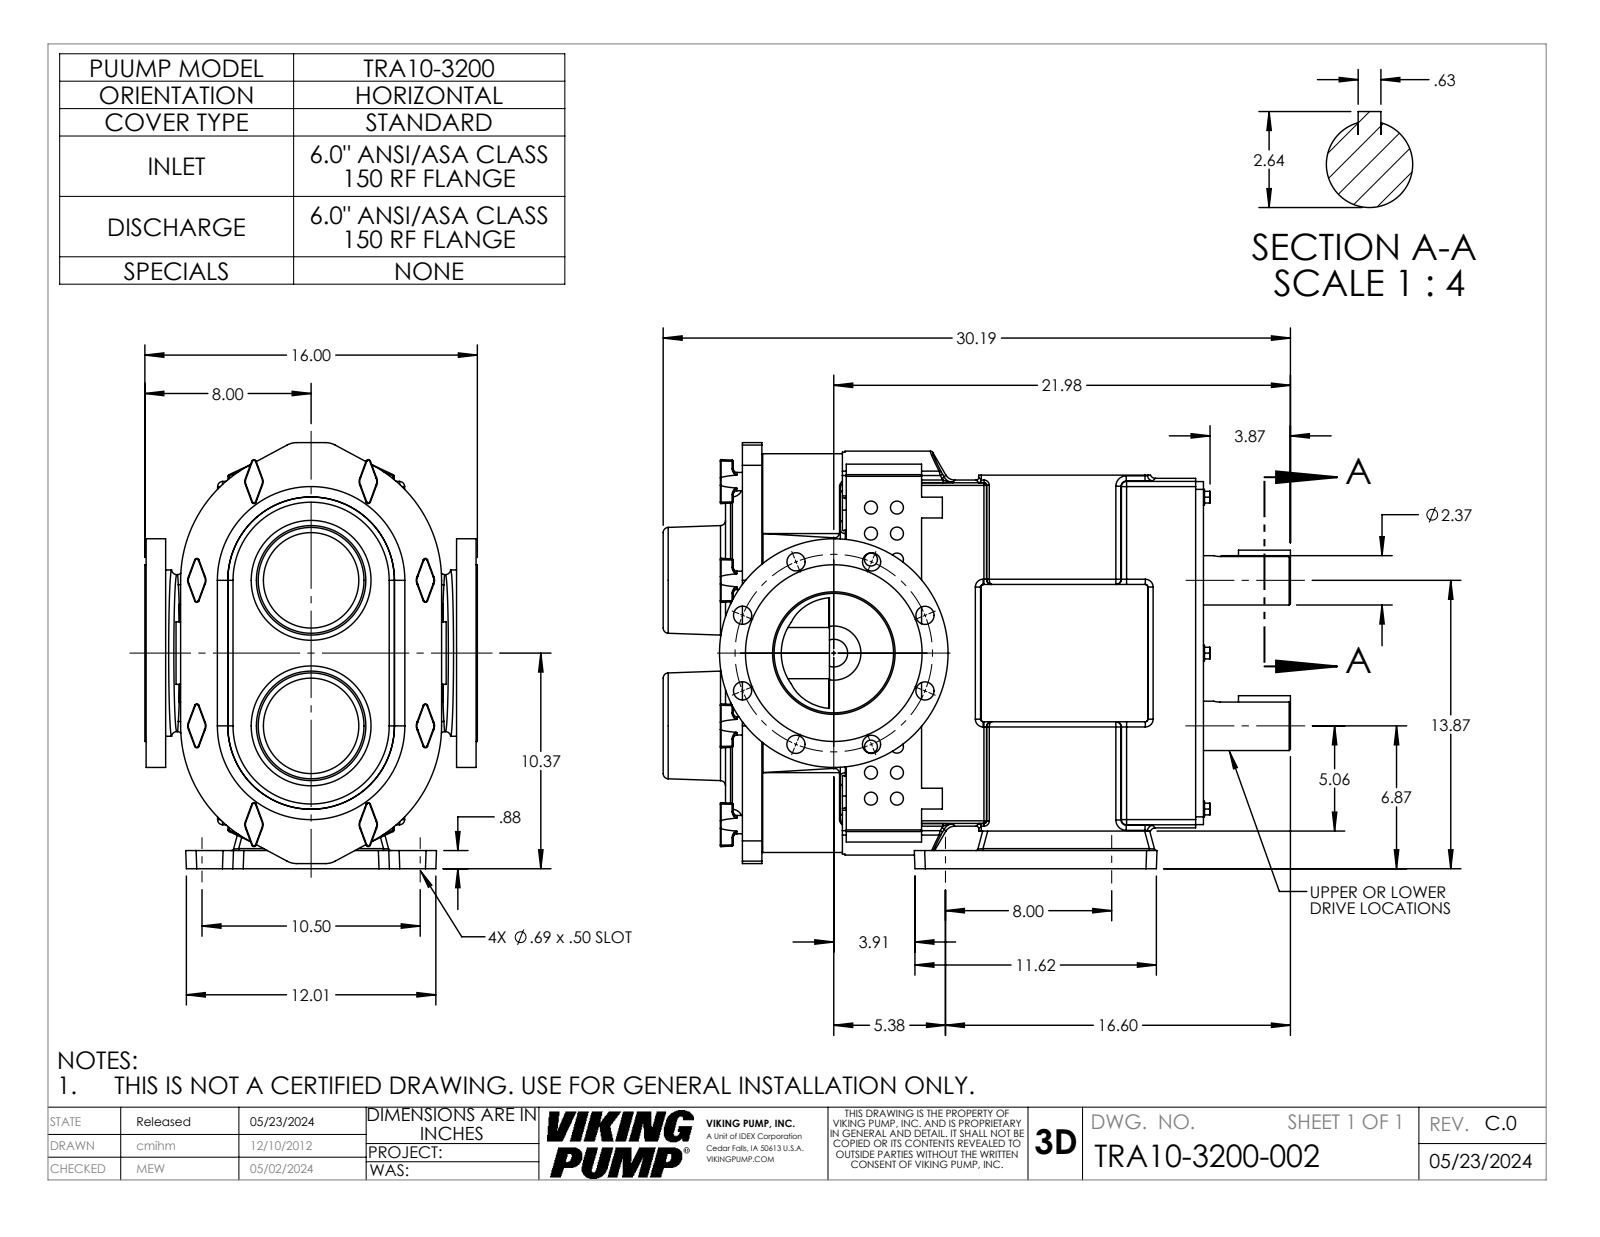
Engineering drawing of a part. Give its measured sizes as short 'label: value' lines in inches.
name: WA3200RCN-60F-60F-00; TRA10-3200-GEARBOX; TRA10-3200-COVER-STD; TRA10-3200-002
written by: SolidWorks 2023 (AUTOMOTIVE_DESIGN)
unit: in
bodies: 3 solids, 1340 faces (342 planar, 476 cylindrical, 522 other)
size: 30.186 × 20.498 × 16
volume: 3 159 in³; area: 3 784 in²
holes: 16× ⌀0.625, 8× ⌀0.313, 8× ⌀0.875, 4× ⌀0.531, 4× ⌀0.687, 2× ⌀0.437, 2× ⌀0.616, 2× ⌀0.625, 2× ⌀4.002, 2× ⌀4.878
bosses: 8× ⌀0.88, 6× ⌀0.75, 2× ⌀4.865, 2× ⌀2.374, 1× ⌀11, 1× ⌀8.5, 1× ⌀8, 1× ⌀7.55
rounds: 66× R0.25, 58× R0.125, 32× R0.03, 32× R0.06, 14× R0.5, 8× R0.344, 4× R0.029, 4× R0.089
face distances: 0.06, 1, 3.5, 11.5, 21.25, 0.438, 7.438, 4.002, 11.938, 0.56
hole spacings: 1.25, 4.035, 7.748, 1.768, 2.813, 3.978, 5.489, 5.5
